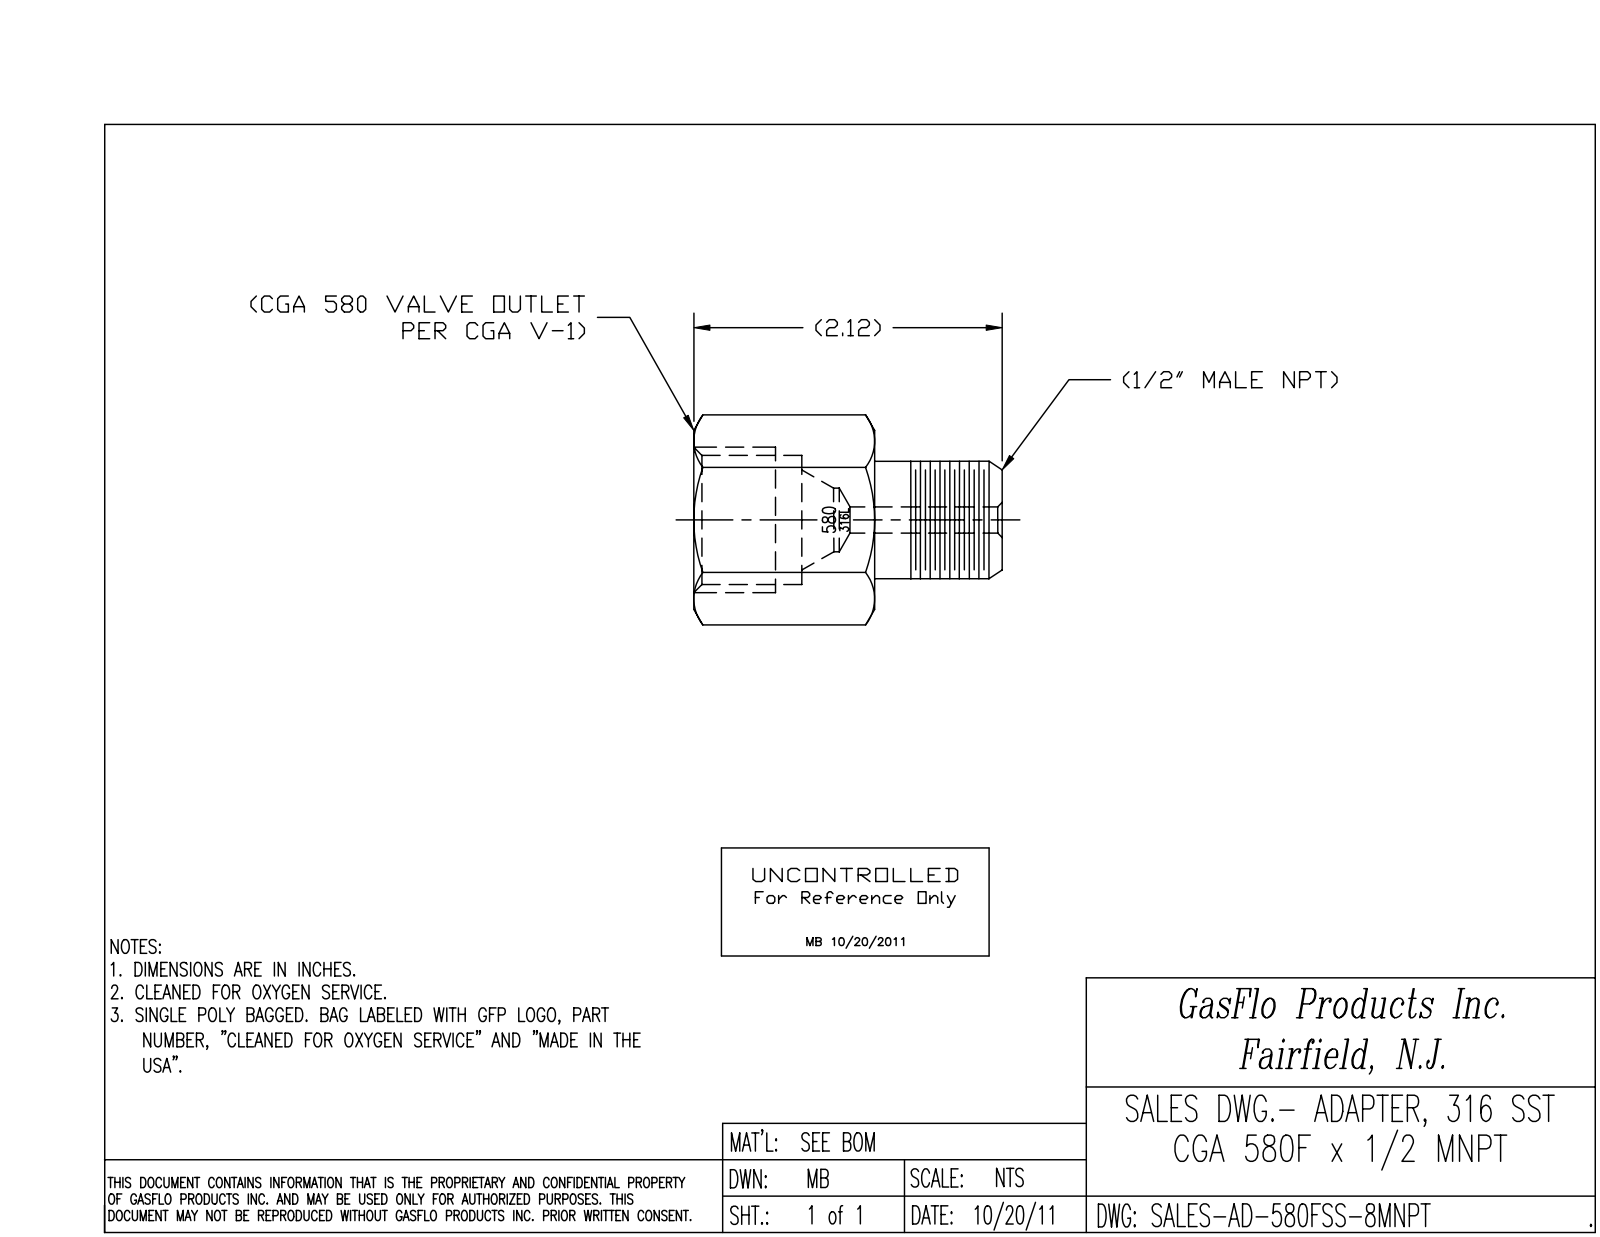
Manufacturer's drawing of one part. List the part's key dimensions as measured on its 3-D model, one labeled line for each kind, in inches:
Part name (STEP PRODUCT): AD-580FSS-8MNPT
STEP written by: SolidWorks 2018 (CONFIG_CONTROL_DESIGN)
Units: inches
Bodies: 1 solid, 161 faces (38 planar, 22 cylindrical, 101 other)
Overall size (bounding box): 2.12 × 1.443 × 1.25
Volume: 1.339 in³ · Surface area: 14.7 in²
Round holes (diameter × count): ⌀0.187 ×1, ⌀0.422 ×1, ⌀0.892 ×1
Round bosses / shafts (diameter × count): ⌀0.84 ×1
Main face-to-face distances: 1.25, 1.25, 0.995, 1.125, 2.12, 1.433, 0.308, 0.687, 1.24, 1.499
